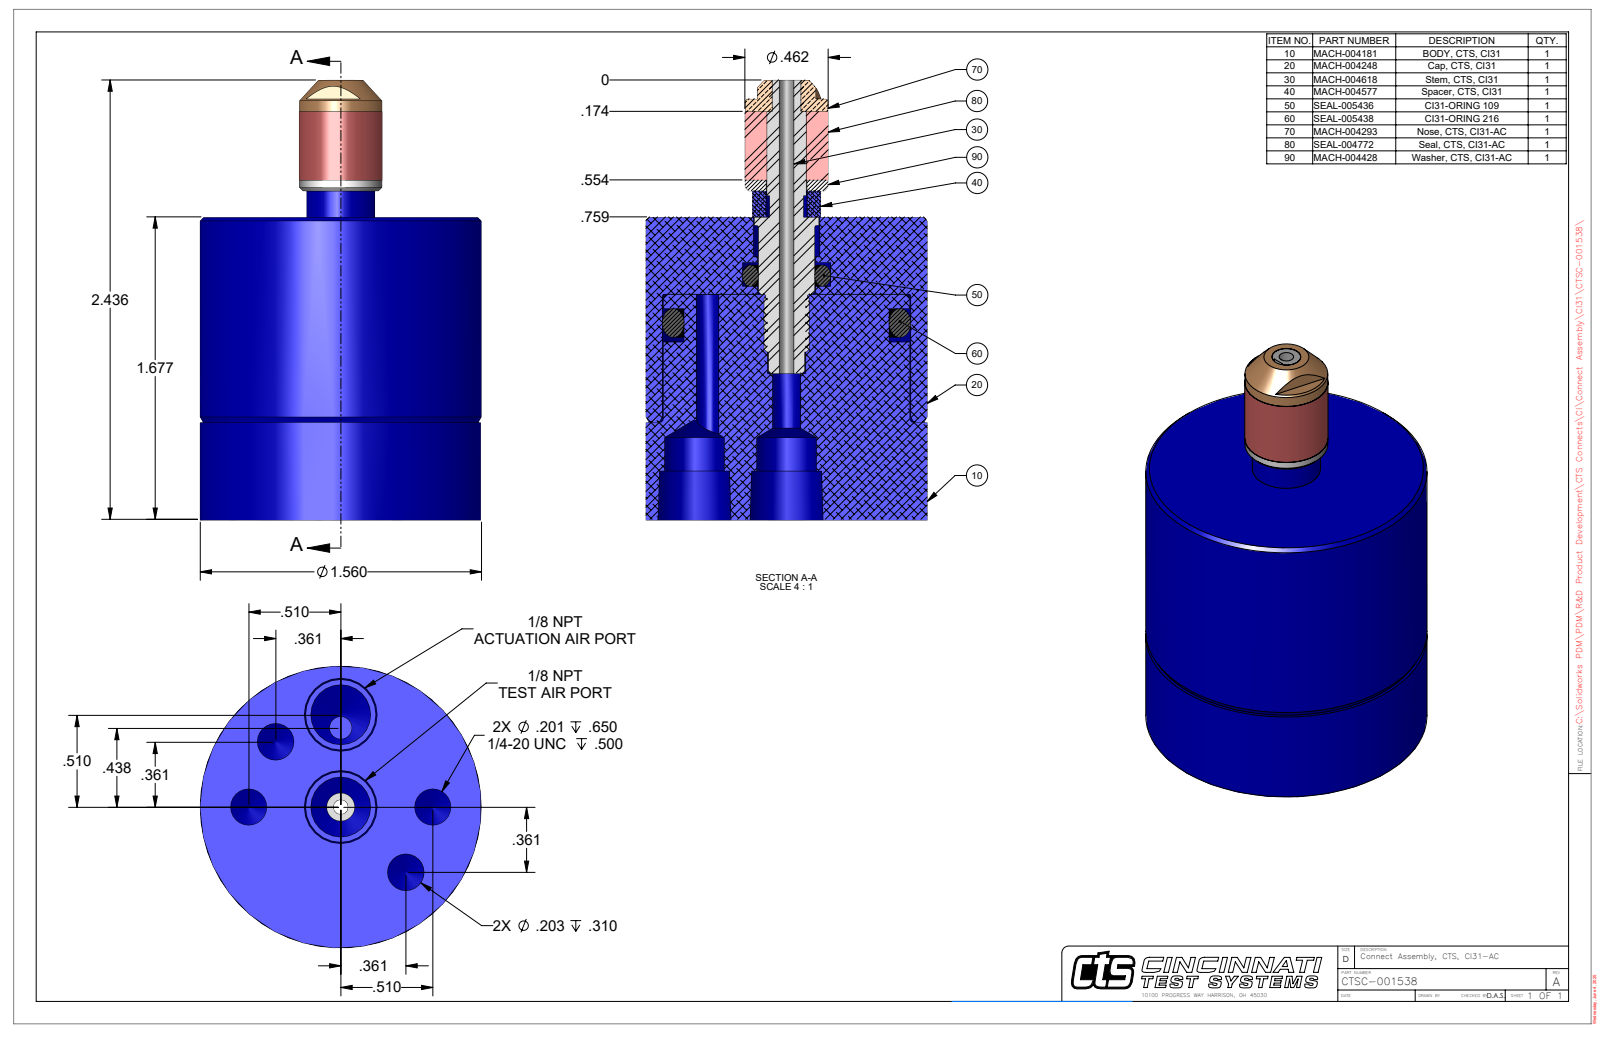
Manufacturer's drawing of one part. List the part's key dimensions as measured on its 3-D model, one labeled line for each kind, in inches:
Part name (STEP PRODUCT): CTSC-001538
STEP written by: SolidWorks 2023 (AUTOMOTIVE_DESIGN)
Units: inches
Bodies: 1 solid, 91 faces (23 planar, 38 cylindrical, 30 other)
Overall size (bounding box): 2.437 × 1.56 × 1.56
Volume: 3.119 in³ · Surface area: 18.61 in²
Round holes (diameter × count): ⌀0.201 ×2, ⌀0.203 ×2, ⌀0.332 ×2, ⌀0.081 ×1, ⌀0.125 ×1, ⌀0.156 ×1, ⌀0.368 ×1, ⌀1.377 ×1
Round bosses / shafts (diameter × count): ⌀1.56 ×1, ⌀1.365 ×1, ⌀0.462 ×1, ⌀0.46 ×1, ⌀0.379 ×1, ⌀0.357 ×1
Main face-to-face distances: 1.677, 0.542, 1.135, 0.812, 0.27, 0.865, 0.273, 0.269, 0.539, 1.404
Hole centre spacings: 0.51, 0.39, 0.942, 0.672, 0.721, 0.072, 0.369, 0.437
